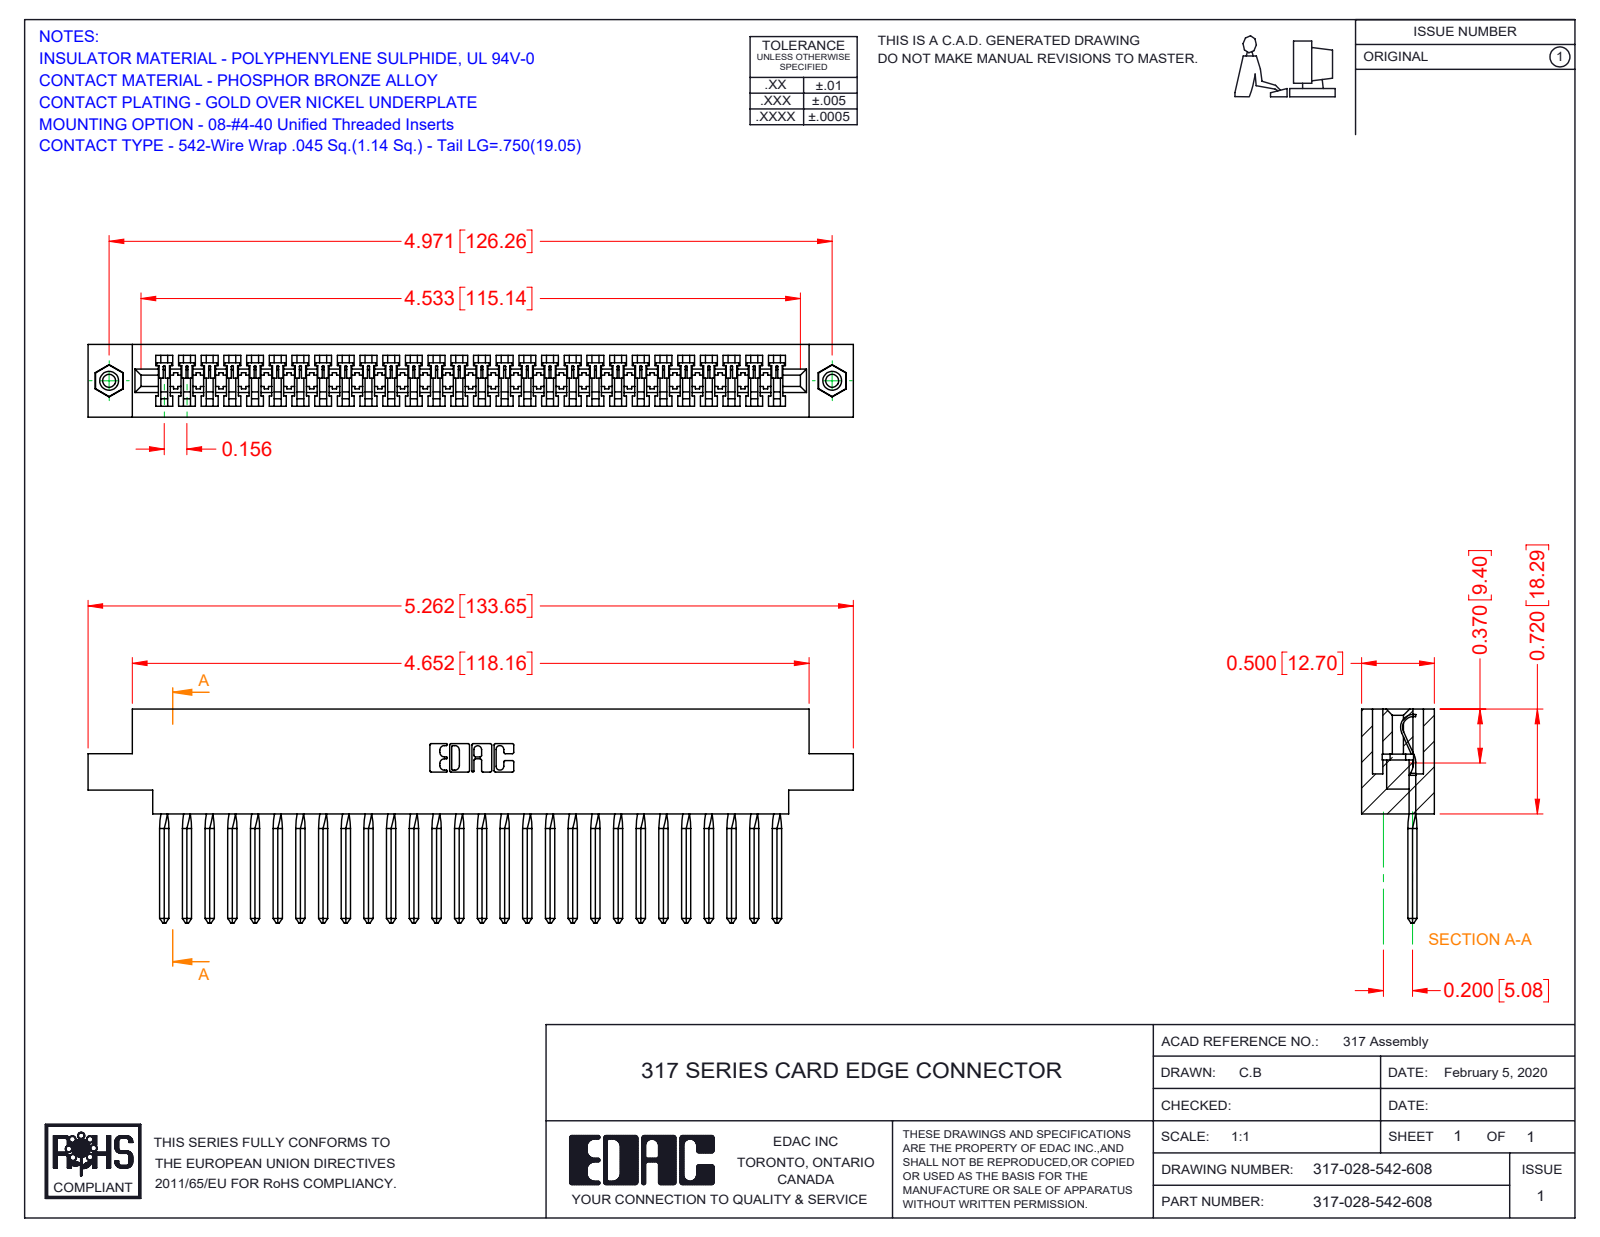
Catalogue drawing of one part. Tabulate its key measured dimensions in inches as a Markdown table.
| quantity | value |
| --- | --- |
| part name | 317-028-542-678; 345-250-001_345-250-003-102; 317 Part_.156 Dia - TI; 317-290-003_542 |
| STEP written by | SolidWorks 2016 (CONFIG_CONTROL_DESIGN) |
| units | inches |
| bodies | 31 solids, 2262 faces (1882 planar, 252 cylindrical, 128 other) |
| overall size | 5.262 × 1.47 × 0.5 |
| volume | 1.237 in³ |
| surface area | 37.87 in² |
| round holes (diameter × count) | 0.089 × 2, 0.125 × 2, 0.156 × 2 |
| round bosses / shafts (diameter × count) | 0.155 × 2 |
| partial cylindrical surfaces (radius × count) | 0.006 × 56, 0.01 × 22, 0.007 × 6, 0.031 × 6, 0.026 × 3, 0.074 × 1, 0.089 × 1, 0.1 × 1 |
| main face-to-face distances | 0.5, 0.075, 0.425, 0.35, 0.11, 0.136, 0.72, 0.279, 0.211, 0.289 |
| hole center spacings | 4.971 |
